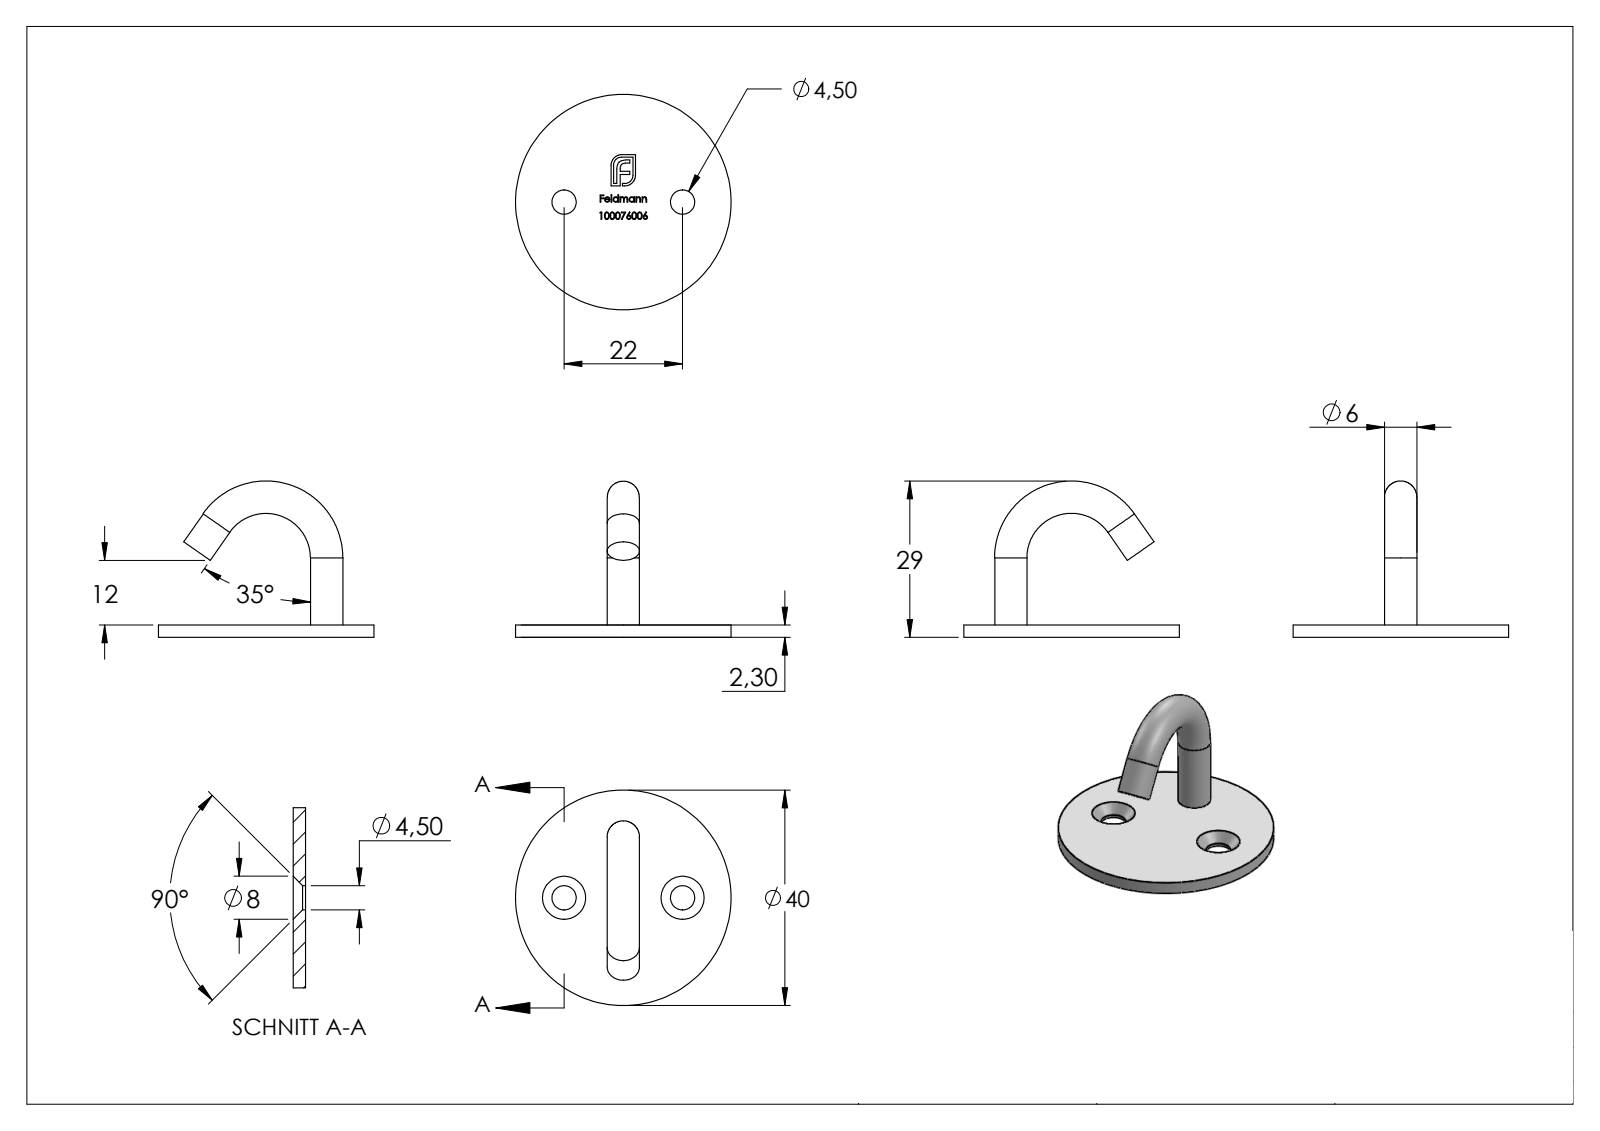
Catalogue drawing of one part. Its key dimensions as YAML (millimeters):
part_name: "100076006"
step_written_by: "SolidWorks 2018 (CONFIG_CONTROL_DESIGN)"
units: millimeters
bodies: {solids: 1, faces: 270, planar: 123, cylindrical: 10, other: 137}
overall_size: [40, 40, 29]
volume: 4097
surface_area: 3688
round_holes:
  - {diameter: 4.5, count: 2}
round_bosses_or_shafts:
  - {diameter: 6, count: 2}
  - {diameter: 40, count: 1}
face_to_face_distances: [2.3, 2.2, 0.46, 5.35, 4.52, 3.11, 2.99, 1.25, 4.07, 0.45]
hole_center_spacings: [22]
